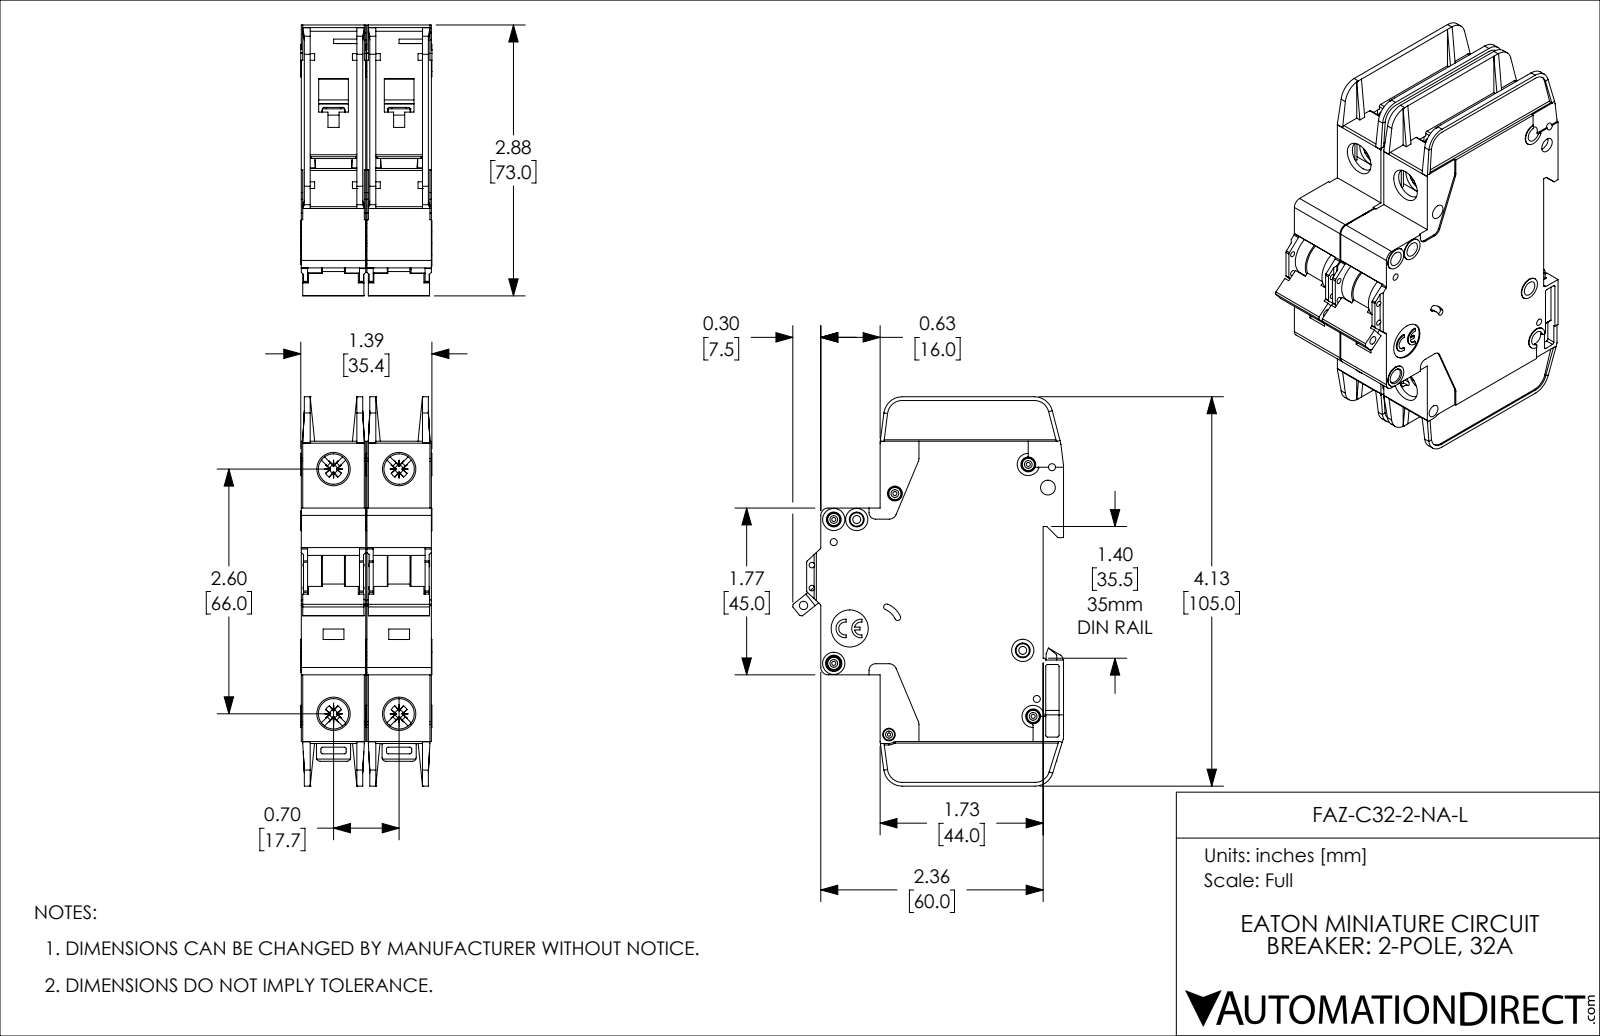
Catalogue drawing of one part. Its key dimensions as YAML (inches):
part_name: "FAZ-C32-2-NA-L"
step_written_by: "SolidWorks 2019 (AUTOMOTIVE_DESIGN)"
units: inches
bodies: {solids: 2, faces: 2254, planar: 1342, cylindrical: 714, other: 198}
overall_size: [4.134, 2.876, 1.394]
volume: 9.365
surface_area: 82.01
round_holes:
  - {diameter: 0.157, count: 8}
  - {diameter: 0.043, count: 5}
  - {diameter: 0.075, count: 4}
  - {diameter: 0.323, count: 4}
  - {diameter: 0.059, count: 2}
  - {diameter: 0.085, count: 2}
  - {diameter: 0.035, count: 1}
  - {diameter: 0.089, count: 1}
  - {diameter: 0.098, count: 1}
  - {diameter: 0.134, count: 1}
  - {diameter: 0.394, count: 1}
round_bosses_or_shafts:
  - {diameter: 0.13, count: 5}
  - {diameter: 0.236, count: 4}
  - {diameter: 0.118, count: 3}
  - {diameter: 0.098, count: 2}
partial_cylinders:
  - {radius: 0.02, count: 57}
  - {radius: 0.016, count: 20}
  - {radius: 0.039, count: 14}
  - {radius: 0.079, count: 10}
  - {radius: 0.043, count: 8}
  - {radius: 0.008, count: 5}
  - {radius: 0.197, count: 5}
  - {radius: 0.01, count: 4}
face_to_face_distances: [0.697, 0.047, 0.685, 0.591, 0.094, 0.638, 0.543, 1.382, 0.744, 0.65]
hole_center_spacings: [0.244, 0.537, 0.697, 0.87, 2.598, 2.69, 0.189, 0.199]
